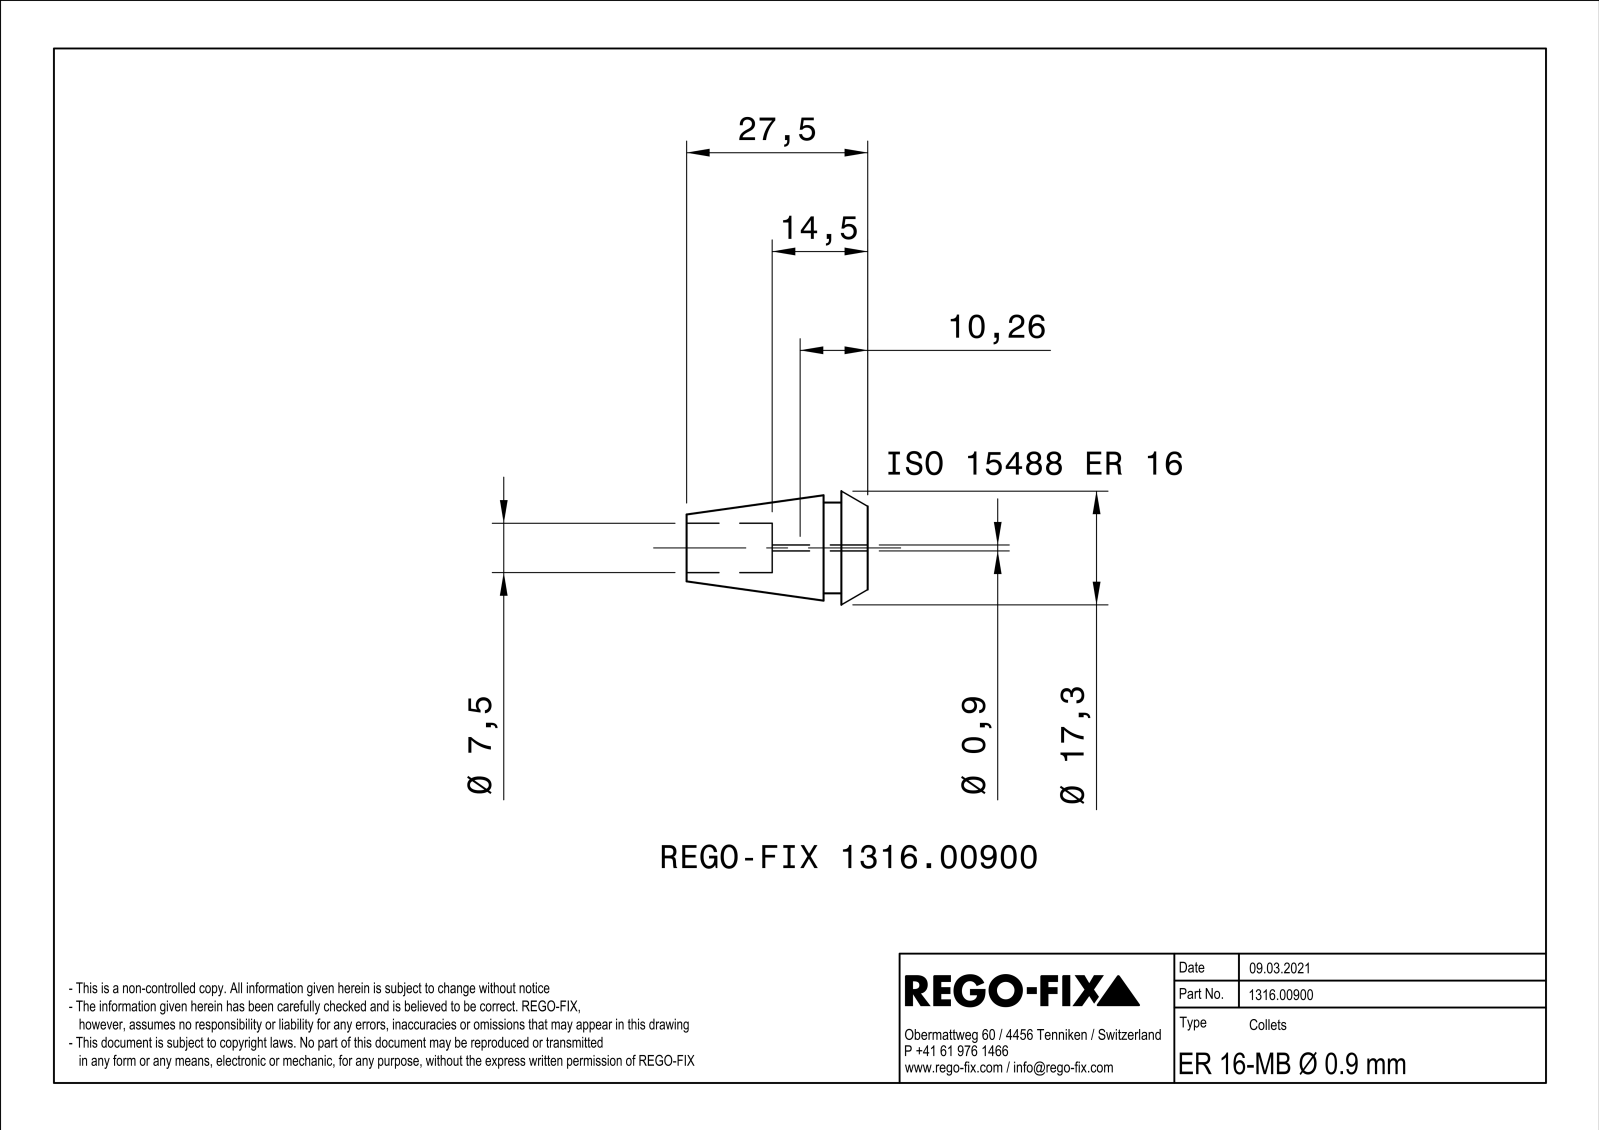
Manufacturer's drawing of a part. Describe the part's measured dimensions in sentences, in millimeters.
The part is named "NOCUT". Its 3-D file was written by "SIEMENS PLM Software Solid Edge ST10 (AUTOMOTIVE_DESIGN)". It is 1 solid with 69 faces: 29 planar, 13 cylindrical and 27 other. Overall it measures 27.5 by 17.25 by 17.25 millimeters. Its volume is 2 960 cubic millimeters and its surface area 2 755 square millimeters. Round holes: 3 of diameter 2, 1 of diameter 7.5. Round bosses or shafts: 1 of diameter 13.8. Partial cylindrical surfaces (rounded edges, fillets, slot ends): 1 of radius 0.45. The main face-to-face distances are 0.8, 4, 0.54, 6.7, 2.7, 27.5, 23.5, 20.8, 14.5, 10.5. The hole center spacings are 2.1, 3.64.
